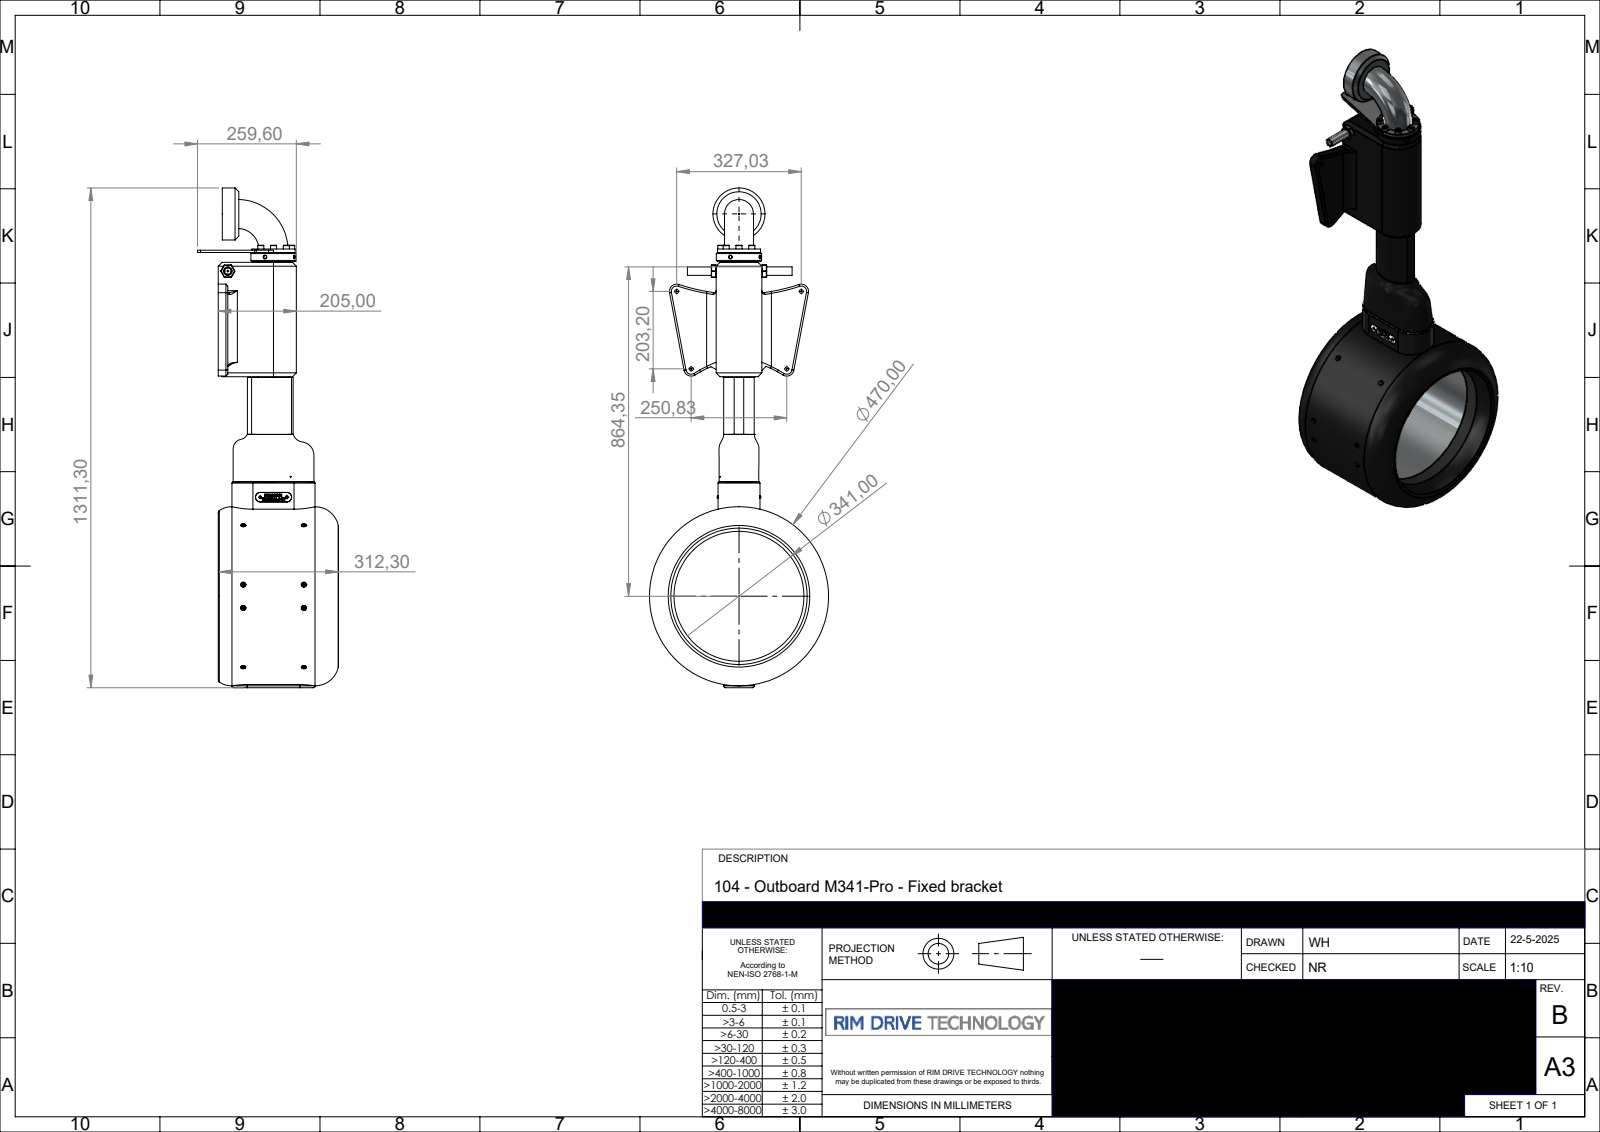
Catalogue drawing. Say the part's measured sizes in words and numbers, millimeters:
The part is named "P-104-430-rev-B-M341-Pro". Its 3-D file was written by "SolidWorks 2024 (AUTOMOTIVE_DESIGN)". It is 1 solid with 1528 faces: 832 planar, 271 cylindrical and 425 other. Overall it measures 1311.3 by 470 by 369.74 millimeters. Its volume is 36 390 000 cubic millimeters and its surface area 1 540 000 square millimeters. Round holes: 14 of diameter 6.6, 4 of diameter 8.5, 4 of diameter 10.2, 2 of diameter 4.2, 2 of diameter 10, 1 of diameter 17, 1 of diameter 341, 1 of diameter 360. Round bosses or shafts: 22 of diameter 11.57, 14 of diameter 6, 6 of diameter 16, 2 of diameter 7.6, 2 of diameter 4, 1 of diameter 470, 1 of diameter 136.4, 1 of diameter 119. Partial cylindrical surfaces (rounded edges, fillets, slot ends): 8 of radius 1, 5 of radius 5, 4 of radius 19.05, 4 of radius 25, 2 of radius 3, 2 of radius 10, 2 of radius 12.4, 2 of radius 40. The main face-to-face distances are 25, 120, 5, 10.44, 14.56, 115, 816.1, 1116.1, 300, 6. The hole center spacings are 25, 160.95, 159, 0.43, 50, 81.53, 110.47, 166.68.
